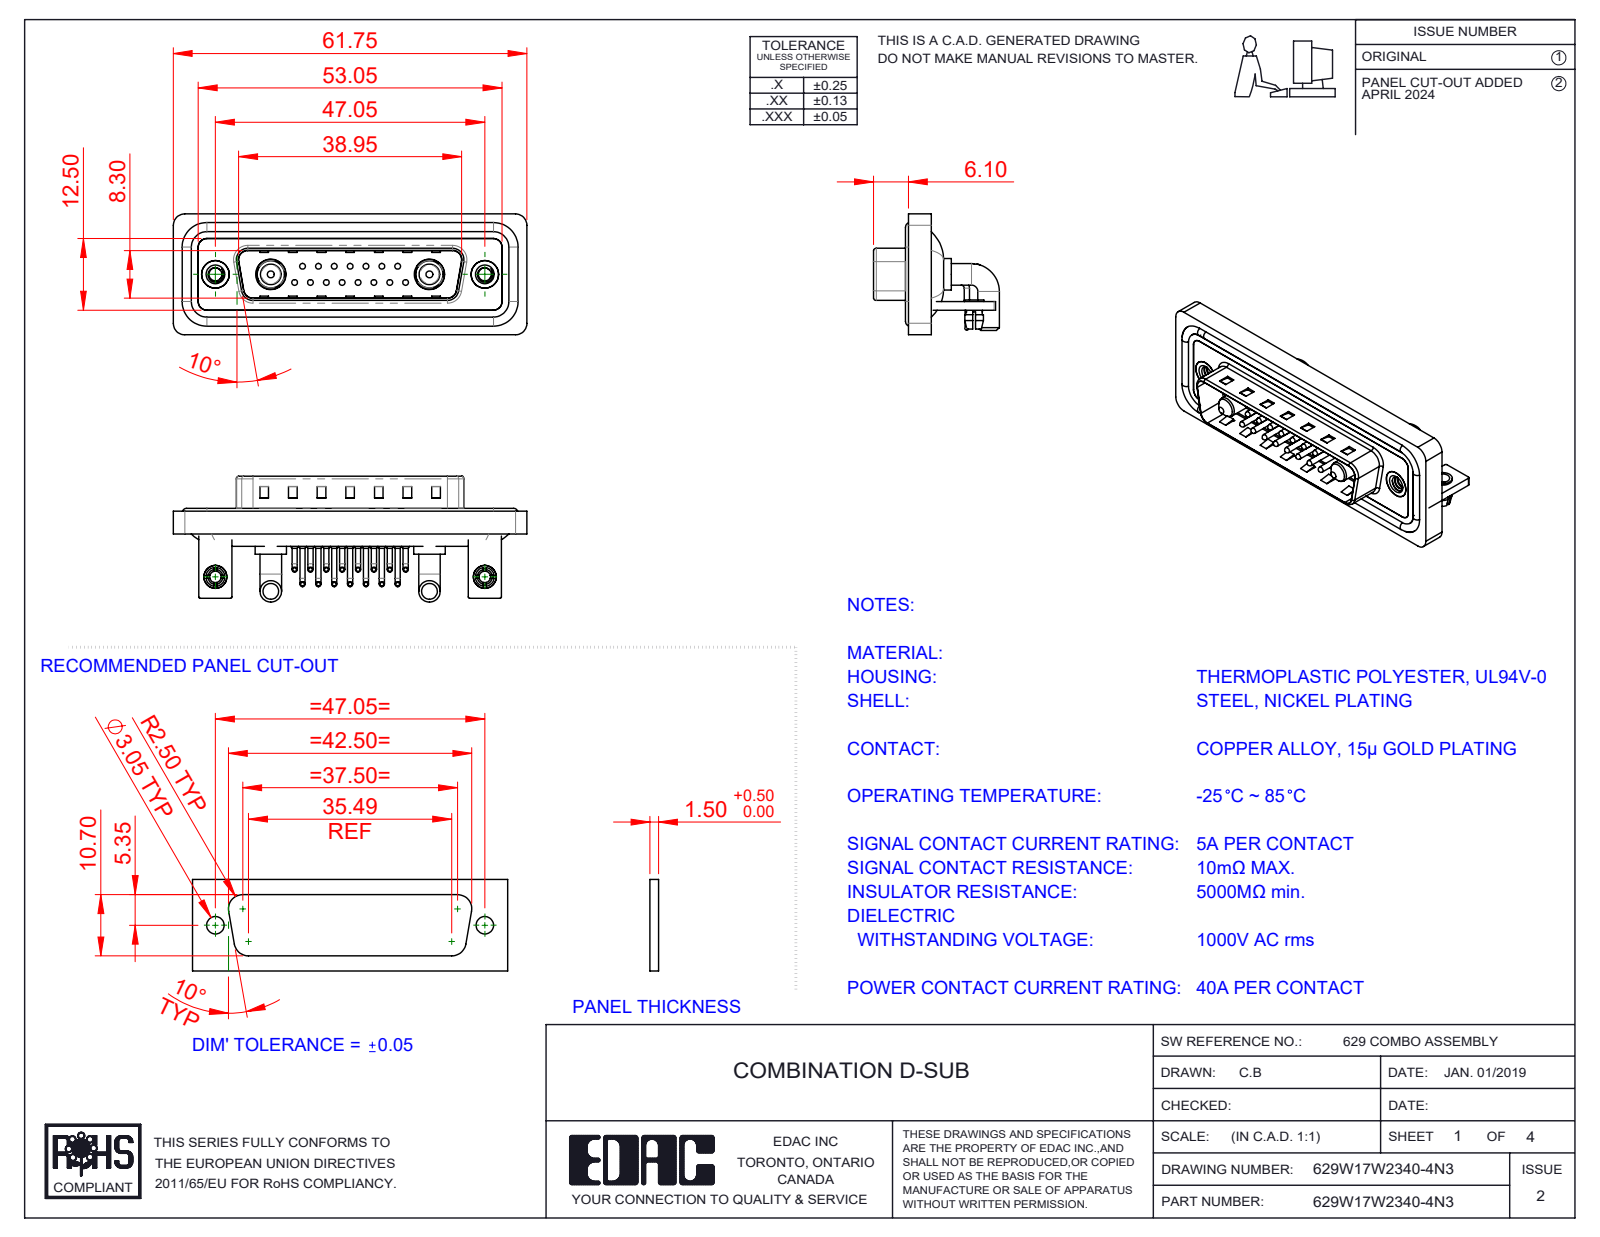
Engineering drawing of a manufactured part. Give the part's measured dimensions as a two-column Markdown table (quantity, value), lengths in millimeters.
| quantity | value |
| --- | --- |
| part name | 629Combo Waterproof Housing_25 Contacts; 629Combo Contact Row 2; 629Combo Shell Rear_25 Contacts; 629Combo Board Lock (+7 more) |
| STEP written by | SolidWorks 2023 (CONFIG_CONTROL_DESIGN) |
| units | millimeters |
| bodies | 30 solids, 2351 faces (1257 planar, 820 cylindrical, 274 other) |
| overall size | 61.75 × 21.98 × 21.1 |
| volume | 7 972 mm³ |
| surface area | 13 486 mm² |
| round holes (diameter × count) | 2 × 17, 0.75 × 15, 1.6 × 15, 2.26 × 2, 2.5 × 2, 3.2 × 2, 4 × 2, 4.8 × 2, 4.85 × 2, 5 × 2, 5.3 × 2 |
| round bosses / shafts (diameter × count) | 0.9 × 30, 1.5 × 15, 1 × 15, 0.65 × 15, 3.75 × 4, 1.6 × 4, 5.5 × 2, 5.2 × 2 |
| partial cylindrical surfaces (radius × count) | 2 × 19, 1.5 × 18, 0.25 × 16, 1.01 × 15, 0.5 × 9, 1.6 × 8, 0.6 × 4, 0.65 × 4 |
| main face-to-face distances | 0.4, 0.8, 2.1, 1.5, 2.9, 1.1, 4.1, 1.6, 4.5, 3.7 |
| hole center spacings | 3.16, 2.77, 5.54, 8.31, 5.04, 7.49, 11.08, 5.03 |
